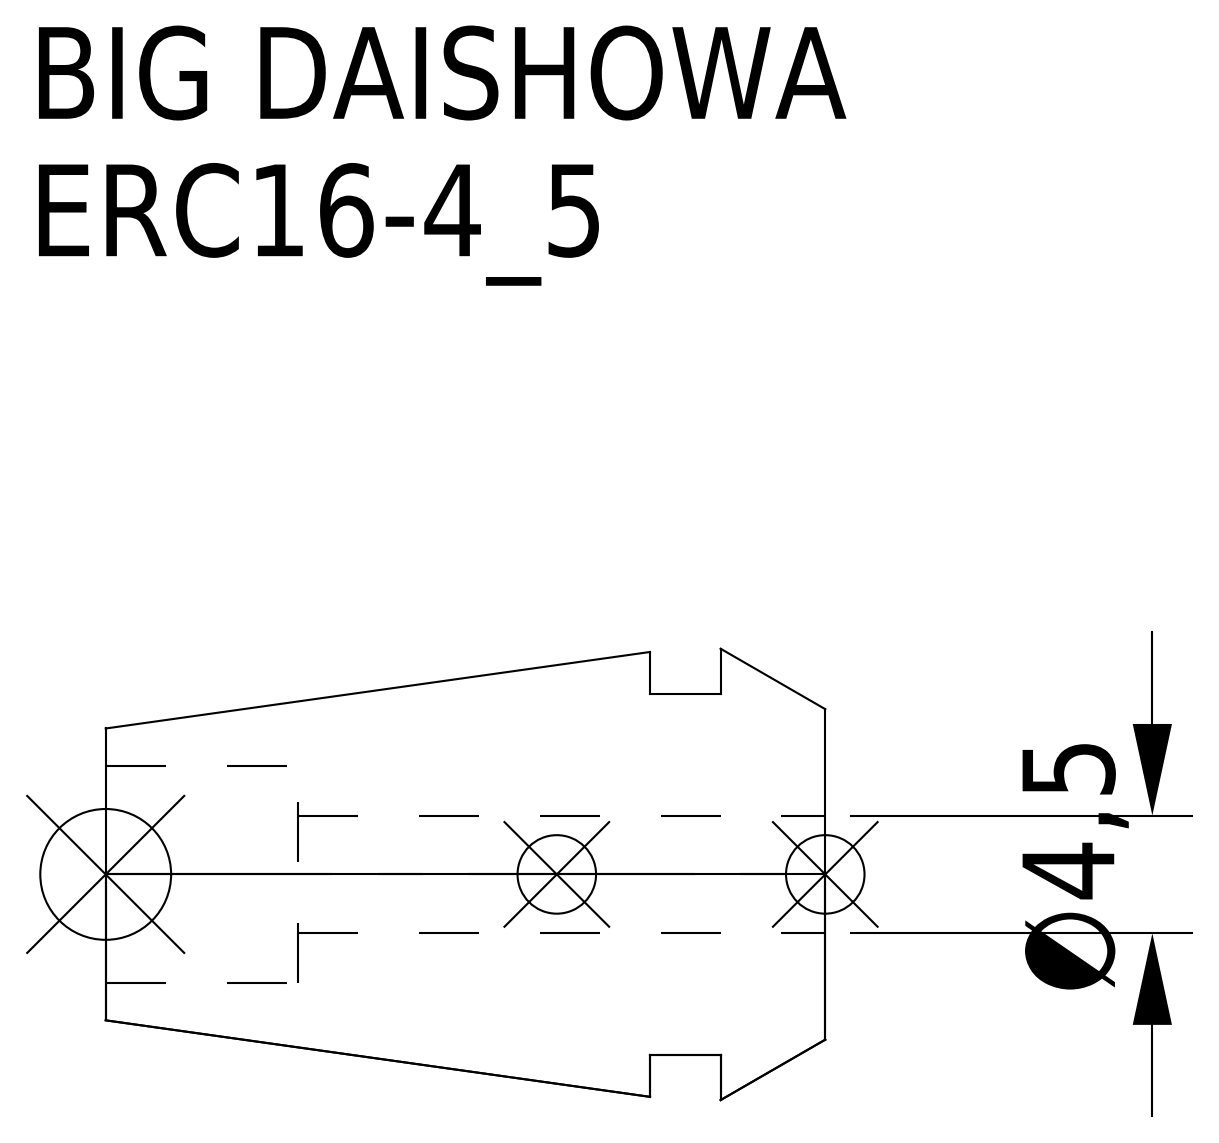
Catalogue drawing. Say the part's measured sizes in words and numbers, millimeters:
The part is named "ERC16-4_5". Its 3-D file was written by "CREO PARAMETRIC BY PTC INC, 2016380 (AUTOMOTIVE_DESIGN)". It is 1 solid with 15 faces: 5 planar, 6 cylindrical and 4 other. Overall it measures 27.5 by 17.25 by 17.25 millimeters. Its volume is 3 677 cubic millimeters and its surface area 2 092 square millimeters. Round holes: 1 of diameter 4.5, 1 of diameter 8.3. Round bosses or shafts: 1 of diameter 13.8. The main face-to-face distances are 4, 6.7, 2.7, 27.5, 23.5, 20.8, 20.16, 16.16, 13.46, 7.34.
